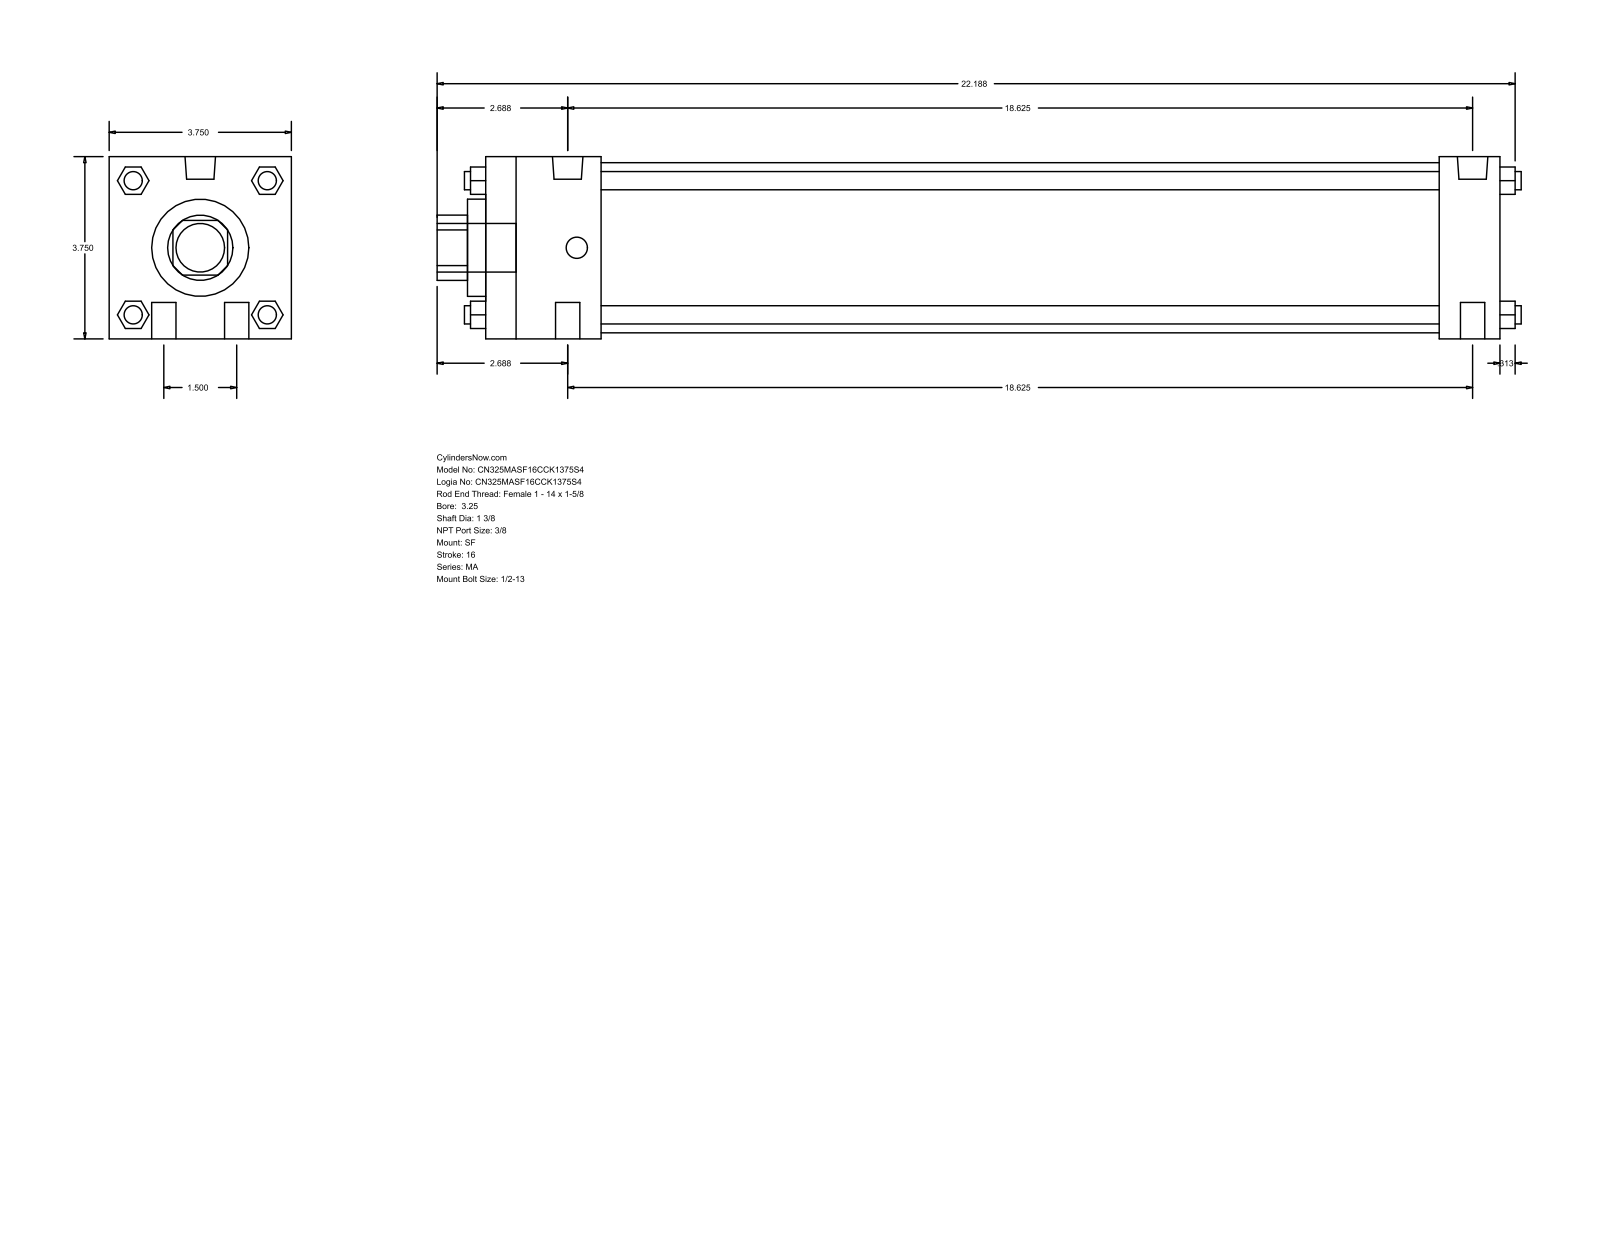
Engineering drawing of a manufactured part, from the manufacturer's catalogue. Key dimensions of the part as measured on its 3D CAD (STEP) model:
Part name (STEP PRODUCT): MA_SF__0325_1.375
STEP written by: GSSL Pune (CONFIG_CONTROL_DESIGN)
Units: millimetres
Bodies: 0 solids, 124 faces (94 planar, 30 cylindrical, 0 other)
Overall size (bounding box): 566.74 × 95.25 × 95.25
Round holes (diameter × count): ⌀34.92 ×1, ⌀50.8 ×1, ⌀88.9 ×1
Round bosses / shafts (diameter × count): ⌀12.7 ×4, ⌀9.53 ×4, ⌀15.93 ×2, ⌀11.11 ×2, ⌀25.4 ×1
Partial cylindrical surfaces — rounded edges, fillets, slot ends (radius × count): R17.06 ×1
Main face-to-face distances: 95.24, 530.22, 498.48, 31.74, 60.32, 438.16, 469.9, 9.52, 69.84, 508
